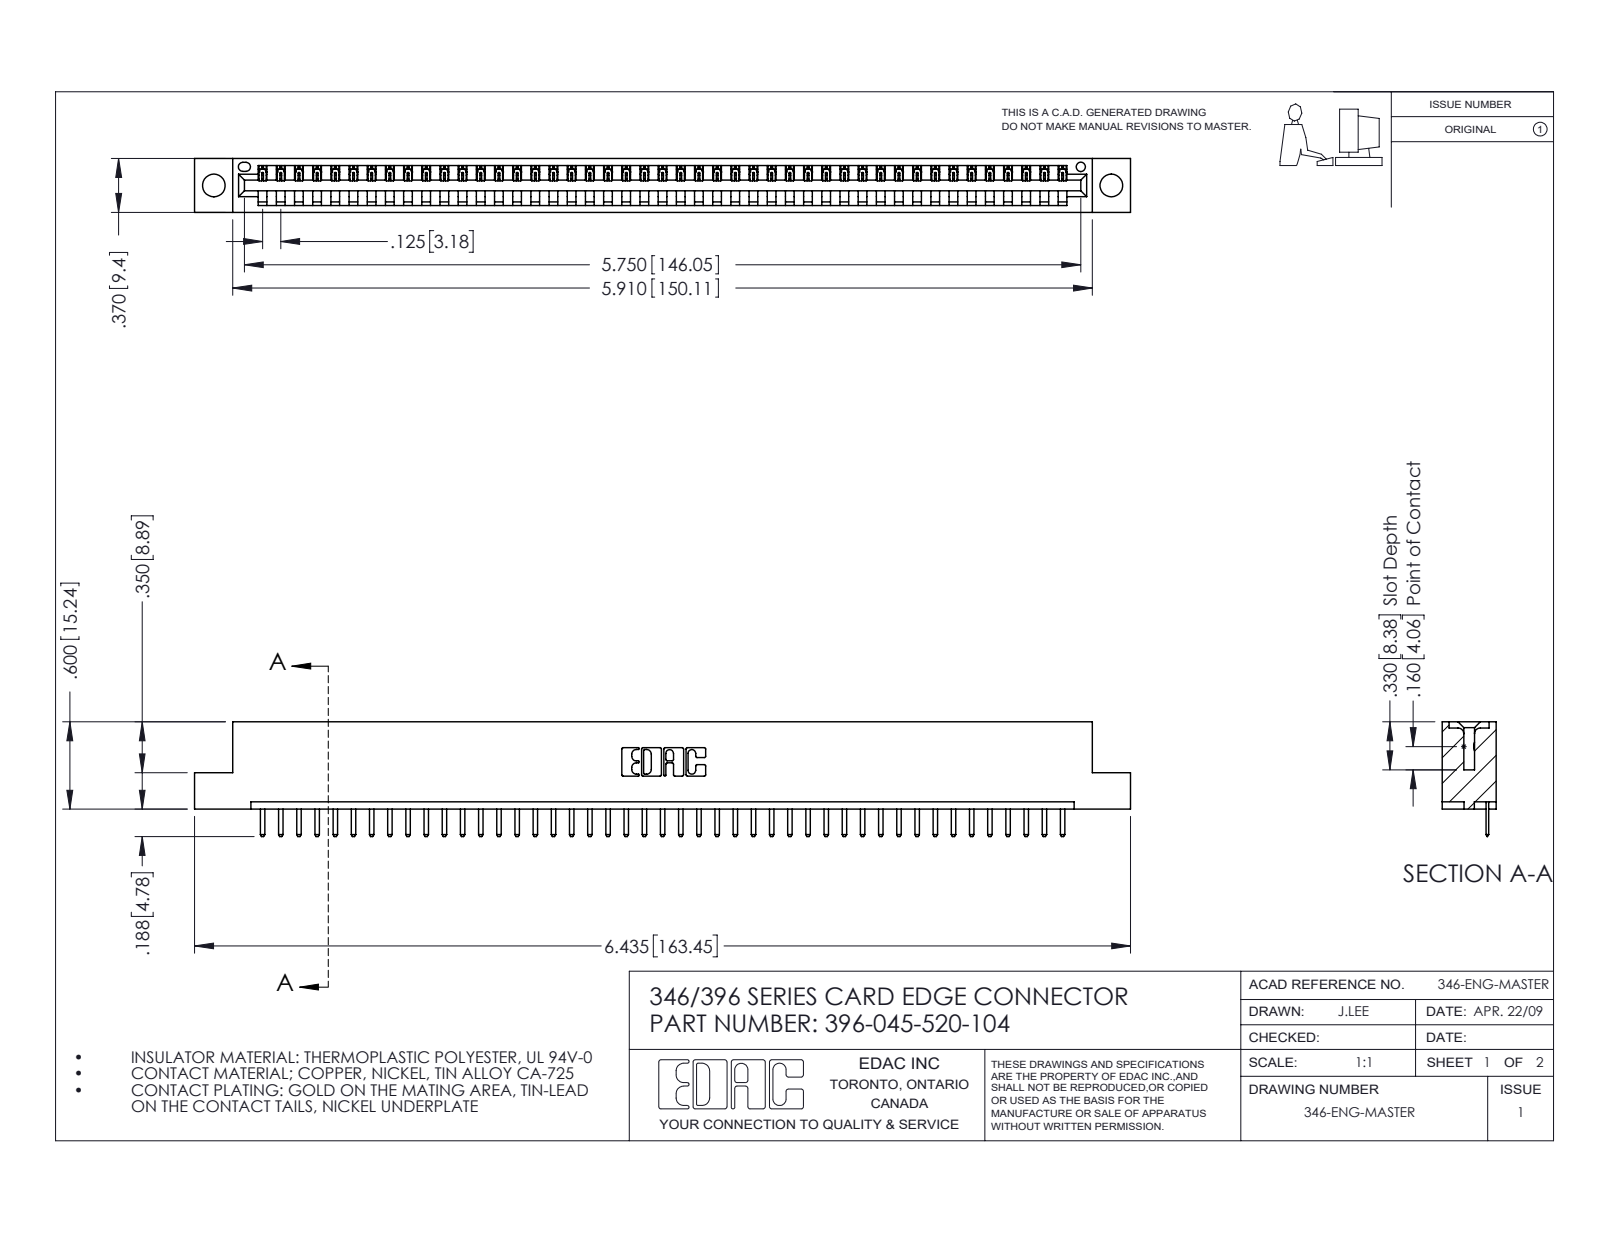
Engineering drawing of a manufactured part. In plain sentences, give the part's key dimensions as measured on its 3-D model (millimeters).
The part is named "396-045-520-104; 346 Part_Flush Mounting Lugs - 0.156 Dia-TH; 345-292-001_345-293-120". Its 3-D file was written by "SolidWorks 2016 (CONFIG_CONTROL_DESIGN)". It is 46 solids with 2912 faces: 1966 planar, 946 cylindrical and 0 other. Overall it measures 163.4 by 20 by 9.4 millimeters. Its volume is 15 500 cubic millimeters and its surface area 18 720 square millimeters. Round holes: 2 of diameter 4, 1 of diameter 1.6. Partial cylindrical surfaces (rounded edges, fillets, slot ends): 92 of radius 0.3, 90 of radius 0.2, 22 of radius 0.3, 6 of radius 0.2, 6 of radius 0.8, 3 of radius 0.7, 2 of radius 0.8, 2 of radius 1. The main face-to-face distances are 1.2, 8.2, 9.4, 6.4, 3.8, 5.6, 2.5, 4.4, 1.8, 7.6. The hole center spacings are 6.2, 151.4, 156.7.
